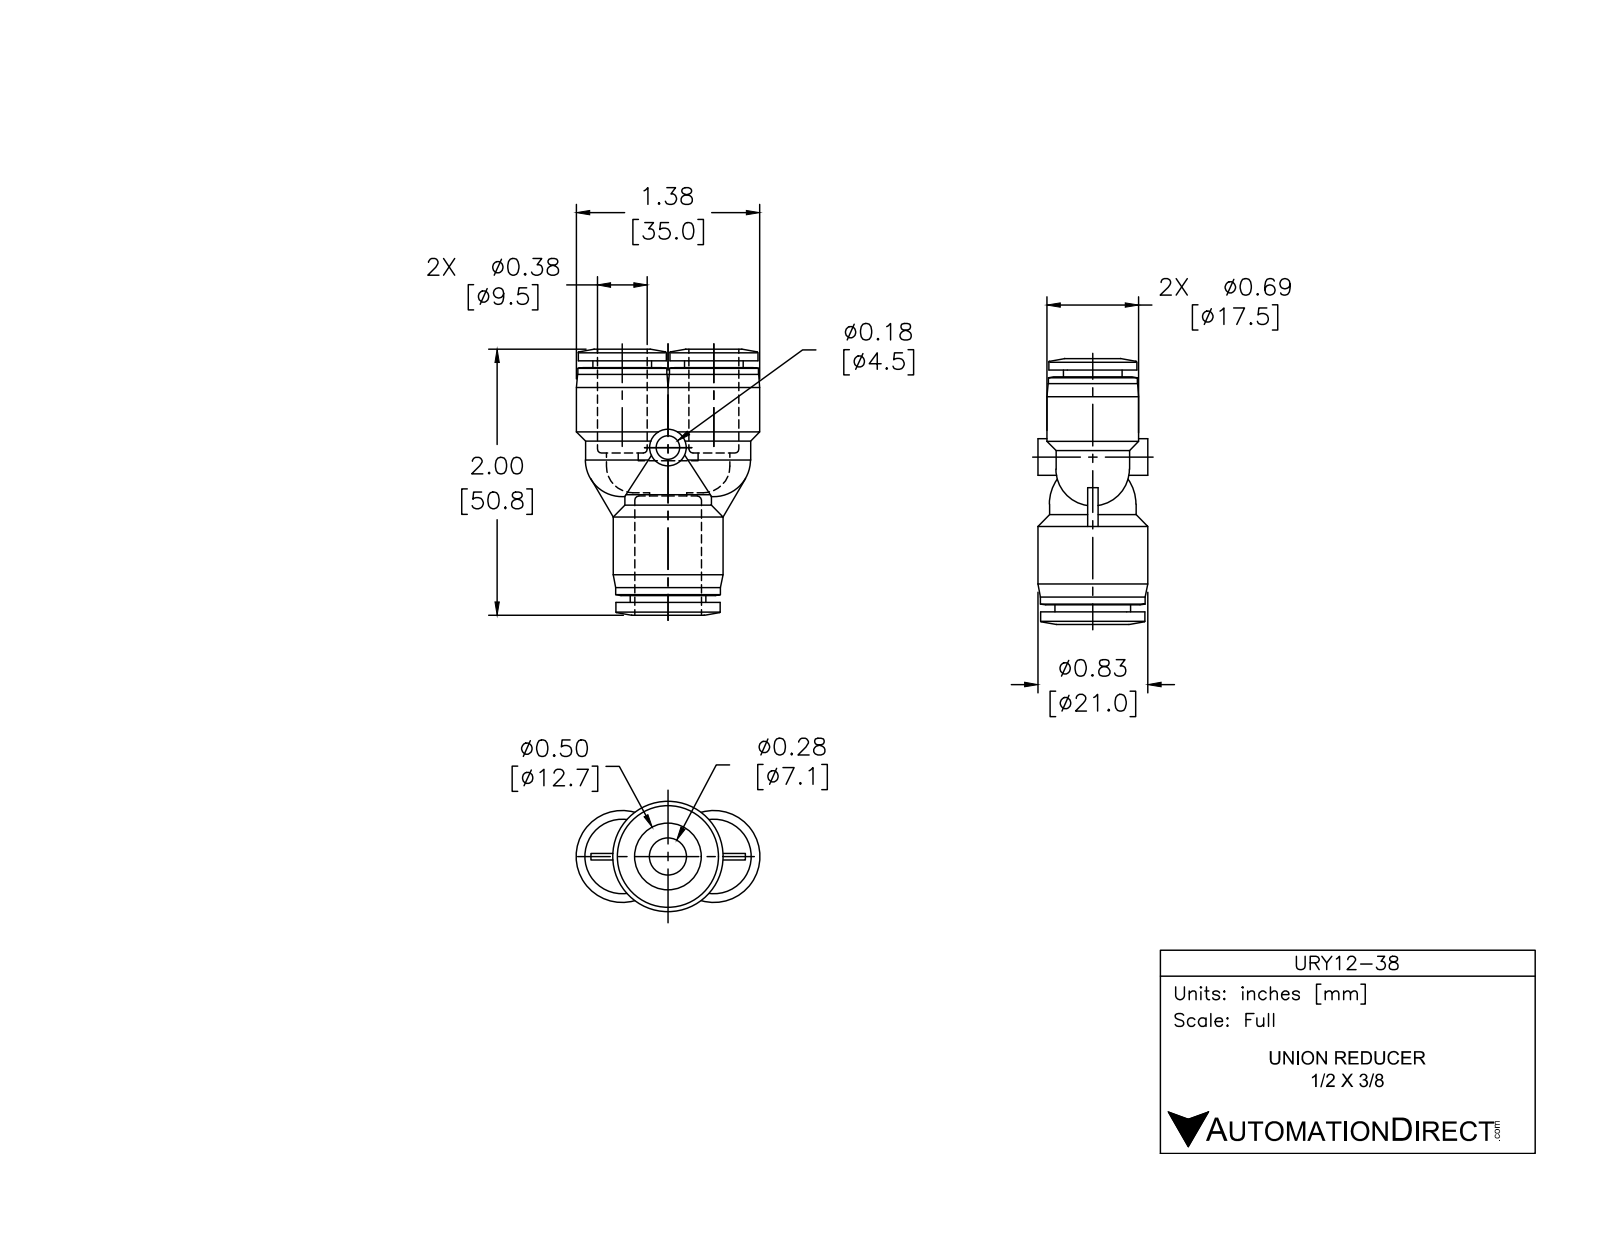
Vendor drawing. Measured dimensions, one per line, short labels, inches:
name: URY12-38
written by: SolidWorks 2015 (AUTOMOTIVE_DESIGN)
unit: in
bodies: 1 solid, 110 faces (18 planar, 41 cylindrical, 51 other)
size: 2 × 1.378 × 0.827
volume: 0.722 in³; area: 13.36 in²
holes: 2× ⌀0.386, 1× ⌀0.177, 1× ⌀0.51
bosses: 2× ⌀0.689, 2× ⌀0.669, 2× ⌀0.661, 2× ⌀0.551, 2× ⌀0.441, 1× ⌀0.827, 1× ⌀0.787, 1× ⌀0.783
face distances: 0.051, 1.766, 1.817, 1.715, 0.809, 0.957, 1.008, 0.758, 1.124, 1.073
hole spacings: 0.344, 0.689
